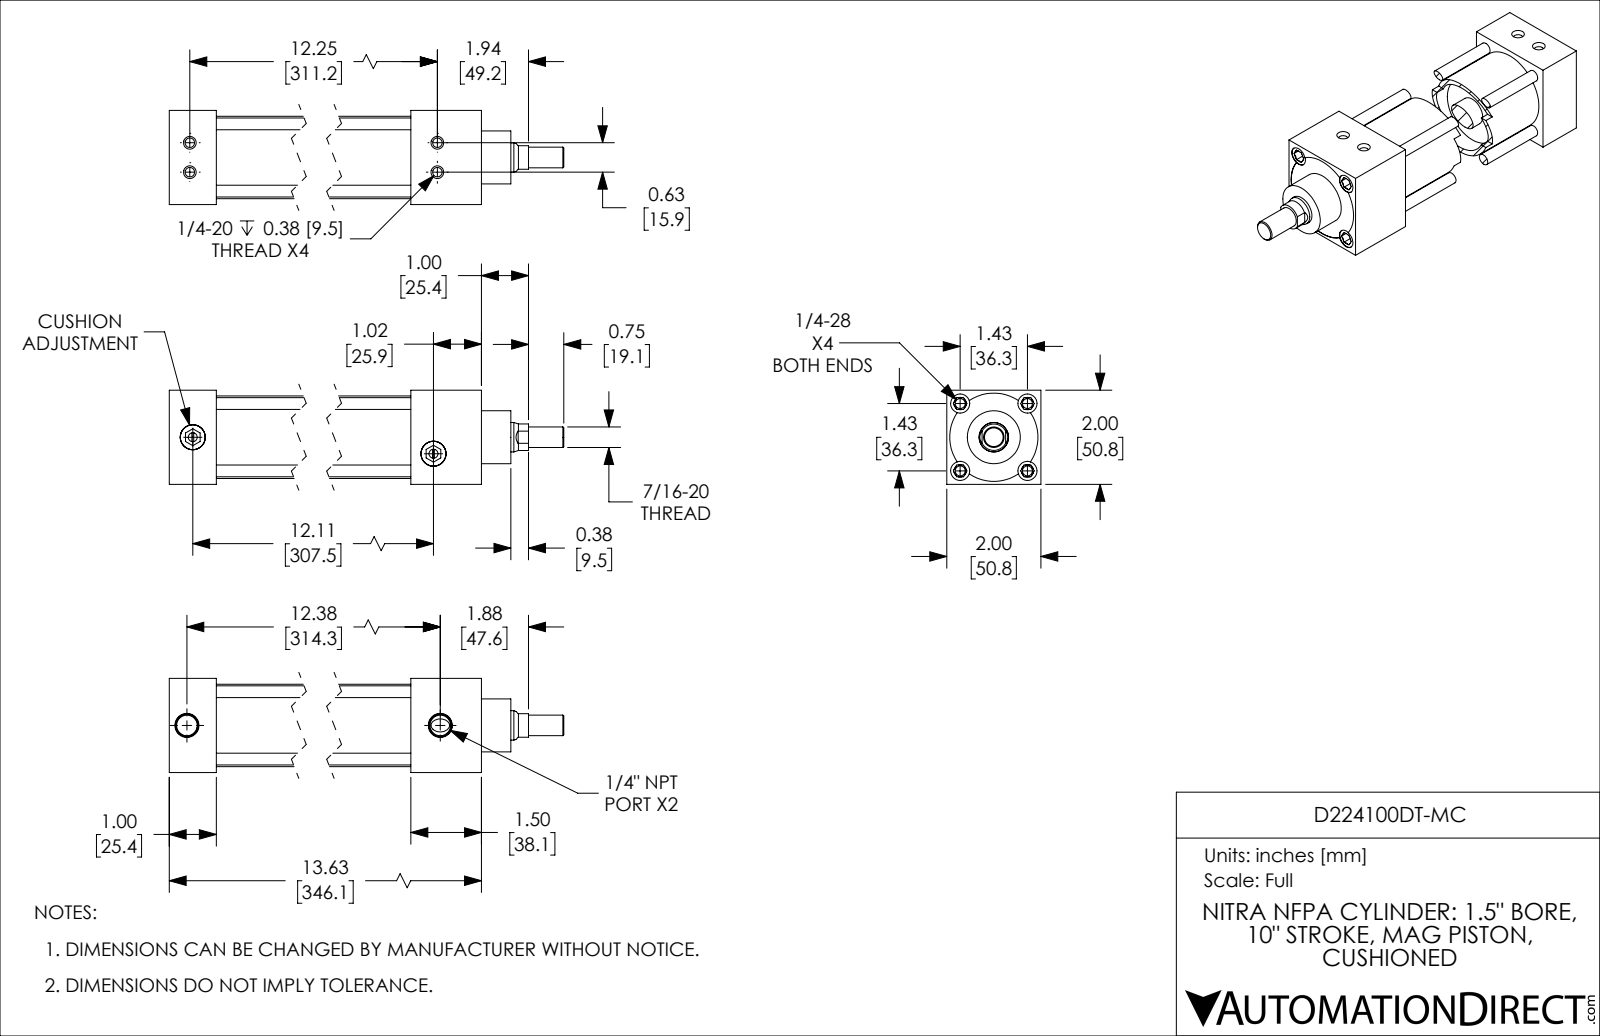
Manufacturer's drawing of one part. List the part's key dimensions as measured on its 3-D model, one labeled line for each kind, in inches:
Part name (STEP PRODUCT): D224100DT-MC_PISTON_KK1; D224100DT-MC; D224100DT-MC_BODY; D224100DT-MC_CUSHION
STEP written by: SolidWorks 2019 (CONFIG_CONTROL_DESIGN)
Units: inches
Bodies: 4 solids, 251 faces (90 planar, 81 cylindrical, 80 other)
Overall size (bounding box): 15.375 × 2 × 2
Volume: 24.58 in³ · Surface area: 232.1 in²
Round holes (diameter × count): ⌀0.201 ×4, ⌀0.213 ×4, ⌀0.406 ×4, ⌀0.19 ×2, ⌀0.438 ×2, ⌀0.531 ×2, ⌀0.626 ×1, ⌀1.501 ×1
Round bosses / shafts (diameter × count): ⌀0.25 ×4, ⌀0.532 ×2, ⌀1.751 ×1, ⌀1.499 ×1, ⌀1.125 ×1, ⌀0.624 ×1, ⌀0.437 ×1
Partial cylindrical surfaces — rounded edges, fillets, slot ends (radius × count): R0.281 ×1, R0.937 ×1
Main face-to-face distances: 2, 1, 12.125, 11.125, 13.62, 12.62, 1.495, 1.125, 2.125, 10
Hole centre spacings: 0.319, 1.011, 1.43, 0.625, 2.022, 12.25, 12.266, 12.316
